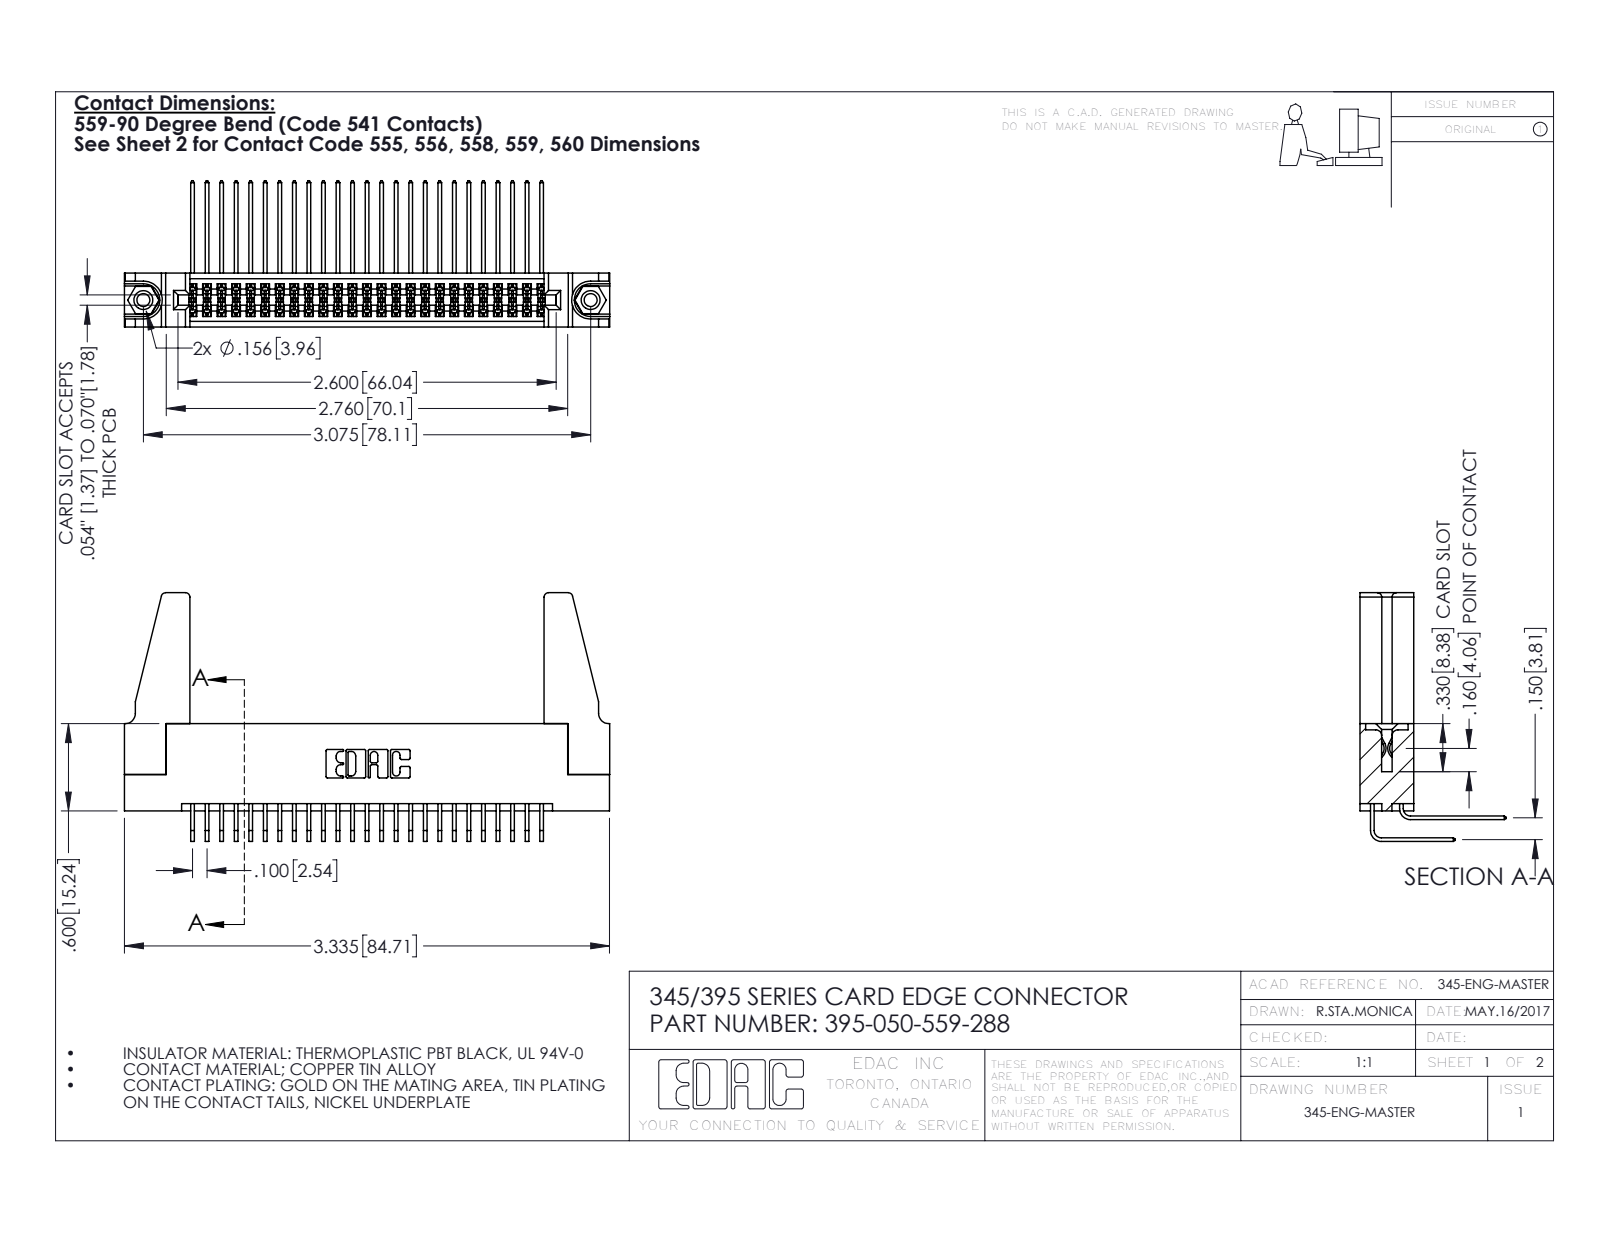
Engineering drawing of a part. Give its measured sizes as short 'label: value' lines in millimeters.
name: 345-292-001_558 559 Tail - 1; 395-050-559-288; 345 Part_Flush Mounting Lugs - 0.156 Dia-TH; 345-250-001_345-250-001-102 (+2 more)
written by: SolidWorks 2016 (CONFIG_CONTROL_DESIGN)
unit: mm
bodies: 55 solids, 2850 faces (1902 planar, 932 cylindrical, 16 other)
size: 84.7 × 43.4 × 25.5
volume: 11 600 mm³; area: 16 510 mm²
holes: 2× ⌀2.3, 2× ⌀3.2, 2× ⌀4, 1× ⌀1.6
bosses: 2× ⌀3.9
rounds: 75× R0.2, 22× R0.3, 8× R0.8, 6× R0.2, 6× R0.8, 3× R0.7, 2× R0.4, 2× R0.5
face distances: 1.8, 7.6, 9.4, 5.1, 2.5, 6.9, 0.6, 5.7, 3.8, 4.4
hole spacings: 6.9, 72.1, 78.1
